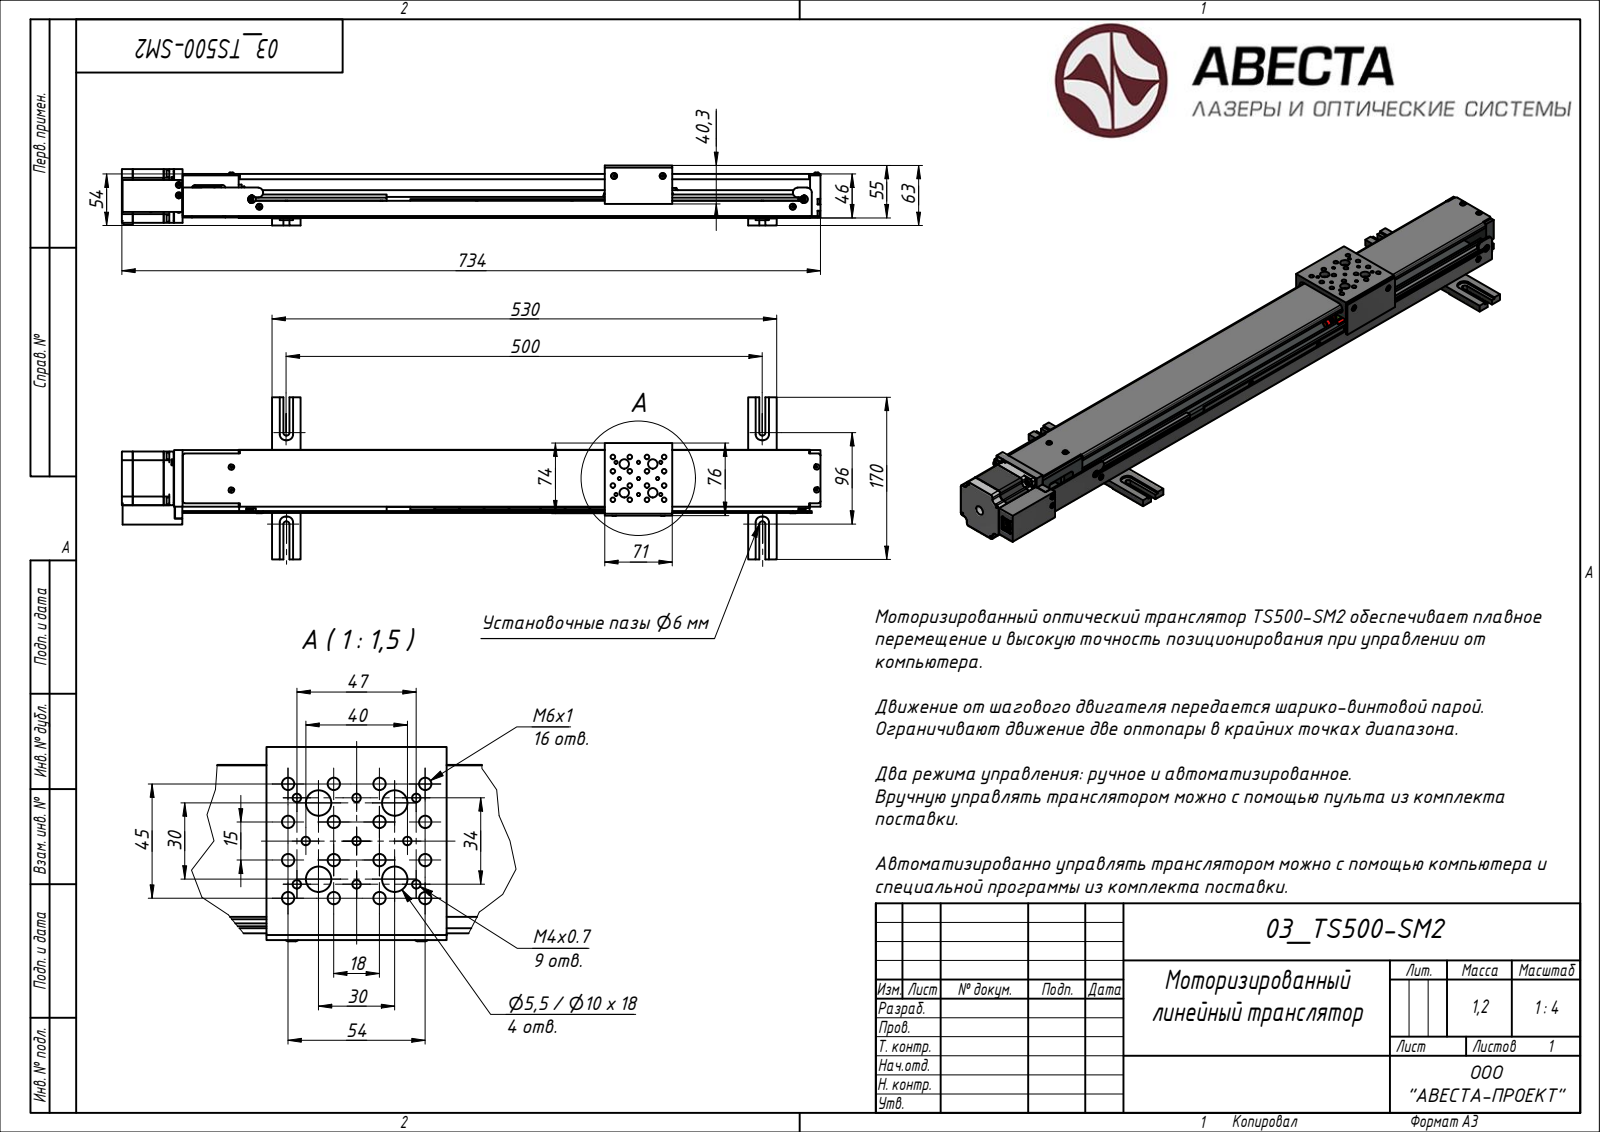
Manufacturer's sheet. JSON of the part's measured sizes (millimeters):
{"step_written_by": "Rhino 7.34 (AUTOMOTIVE_DESIGN)", "units": "millimeters", "bodies": {"solids": 1, "faces": 2511, "planar": 1054, "cylindrical": 806, "other": 651}, "overall_size": [733.9, 170, 63], "volume_mm3": 1106000, "surface_area_mm2": 388331, "round_holes": [[3.24, 14], [5.5, 12], [9.5, 12], [4.13, 8], [6.5, 8], [3.4, 7], [2.11, 6], [10, 5], [1.62, 4], [2.02, 4], [4.92, 4], [2.46, 3]], "round_bosses_or_shafts": [[5.5, 12], [7, 10], [6, 7], [3, 7], [5.7, 4], [4, 4], [2, 4], [1.6, 2]], "partial_cylinders_radius": [[3, 30], [0.5, 16], [2.5, 16], [1.5, 12], [2.46, 11], [2.46, 11], [2, 10], [6, 10]], "face_to_face_distances": [1.5, 0.5, 7.5, 7, 44.5, 44, 45.5, 46, 37, 9], "hole_center_spacings": [30, 15, 11.72, 100, 7, 7.1, 8.73, 15.13]}
